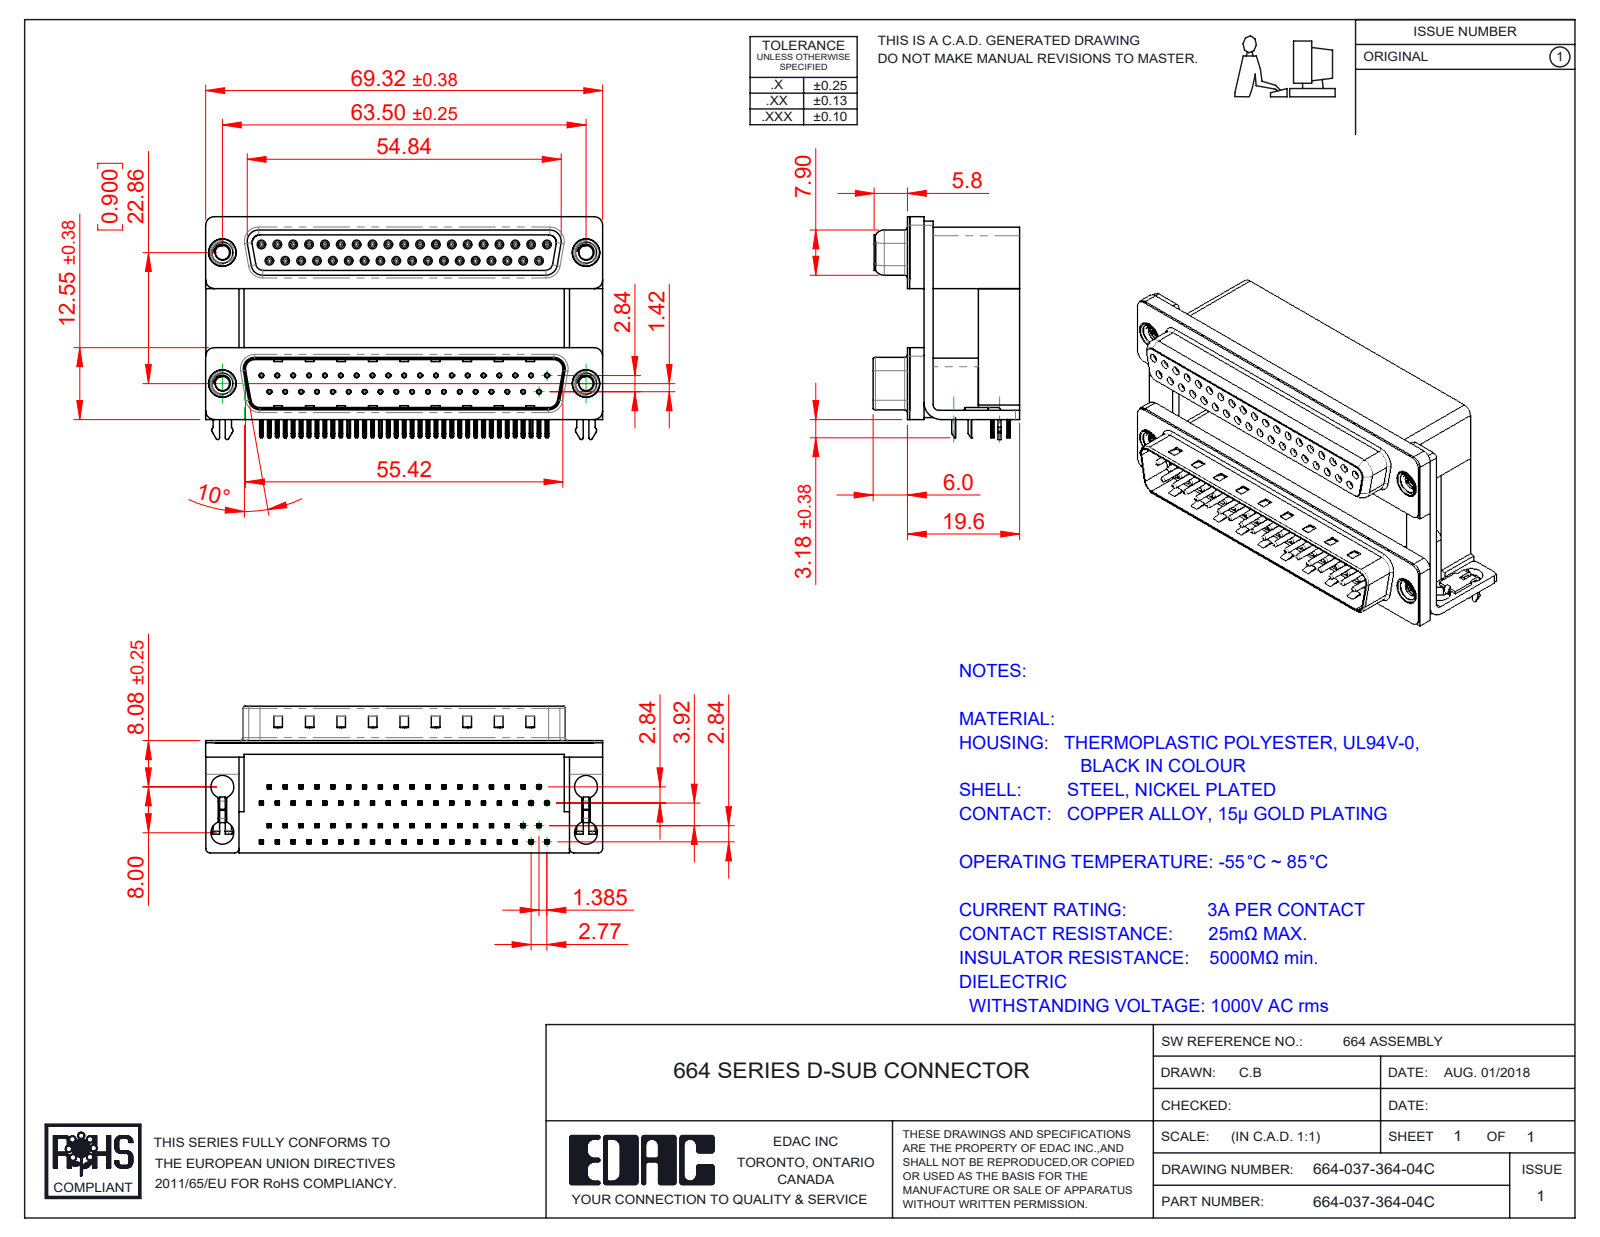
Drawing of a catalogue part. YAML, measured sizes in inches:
part_name: "664 Mounting Bracket_2ProngH; 664 Housing Spacer_37 Contacts H; 664-037-364-04C; 664 Contact Bottom Upper_H (+8 more)"
step_written_by: "SolidWorks 2020 (CONFIG_CONTROL_DESIGN)"
units: inches
bodies: {solids: 87, faces: 9057, planar: 4819, cylindrical: 2215, other: 2023}
overall_size: [2.729, 1.532, 1.008]
volume: 1.993
surface_area: 53.09
round_holes:
  - {diameter: 0.031, count: 74}
  - {diameter: 0.014, count: 37}
  - {diameter: 0.035, count: 37}
  - {diameter: 0.157, count: 8}
  - {diameter: 0.098, count: 4}
  - {diameter: 0.138, count: 4}
  - {diameter: 0.189, count: 4}
  - {diameter: 0.197, count: 4}
round_bosses_or_shafts:
  - {diameter: 0.047, count: 37}
  - {diameter: 0.03, count: 37}
  - {diameter: 0.193, count: 4}
  - {diameter: 0.187, count: 4}
  - {diameter: 0.154, count: 4}
partial_cylinders:
  - {radius: 0.004, count: 297}
  - {radius: 0.01, count: 154}
  - {radius: 0.006, count: 148}
  - {radius: 0.005, count: 74}
  - {radius: 0.014, count: 74}
  - {radius: 0.013, count: 37}
  - {radius: 0.011, count: 18}
  - {radius: 0.02, count: 16}
face_to_face_distances: [0.756, 0.016, 0.472, 0.283, 0.086, 0.112, 0.026, 0.886, 0.421, 0.018]
hole_center_spacings: [0.109, 0.218, 0.124, 0.327, 0.436, 0.545, 0.654, 0.763]
